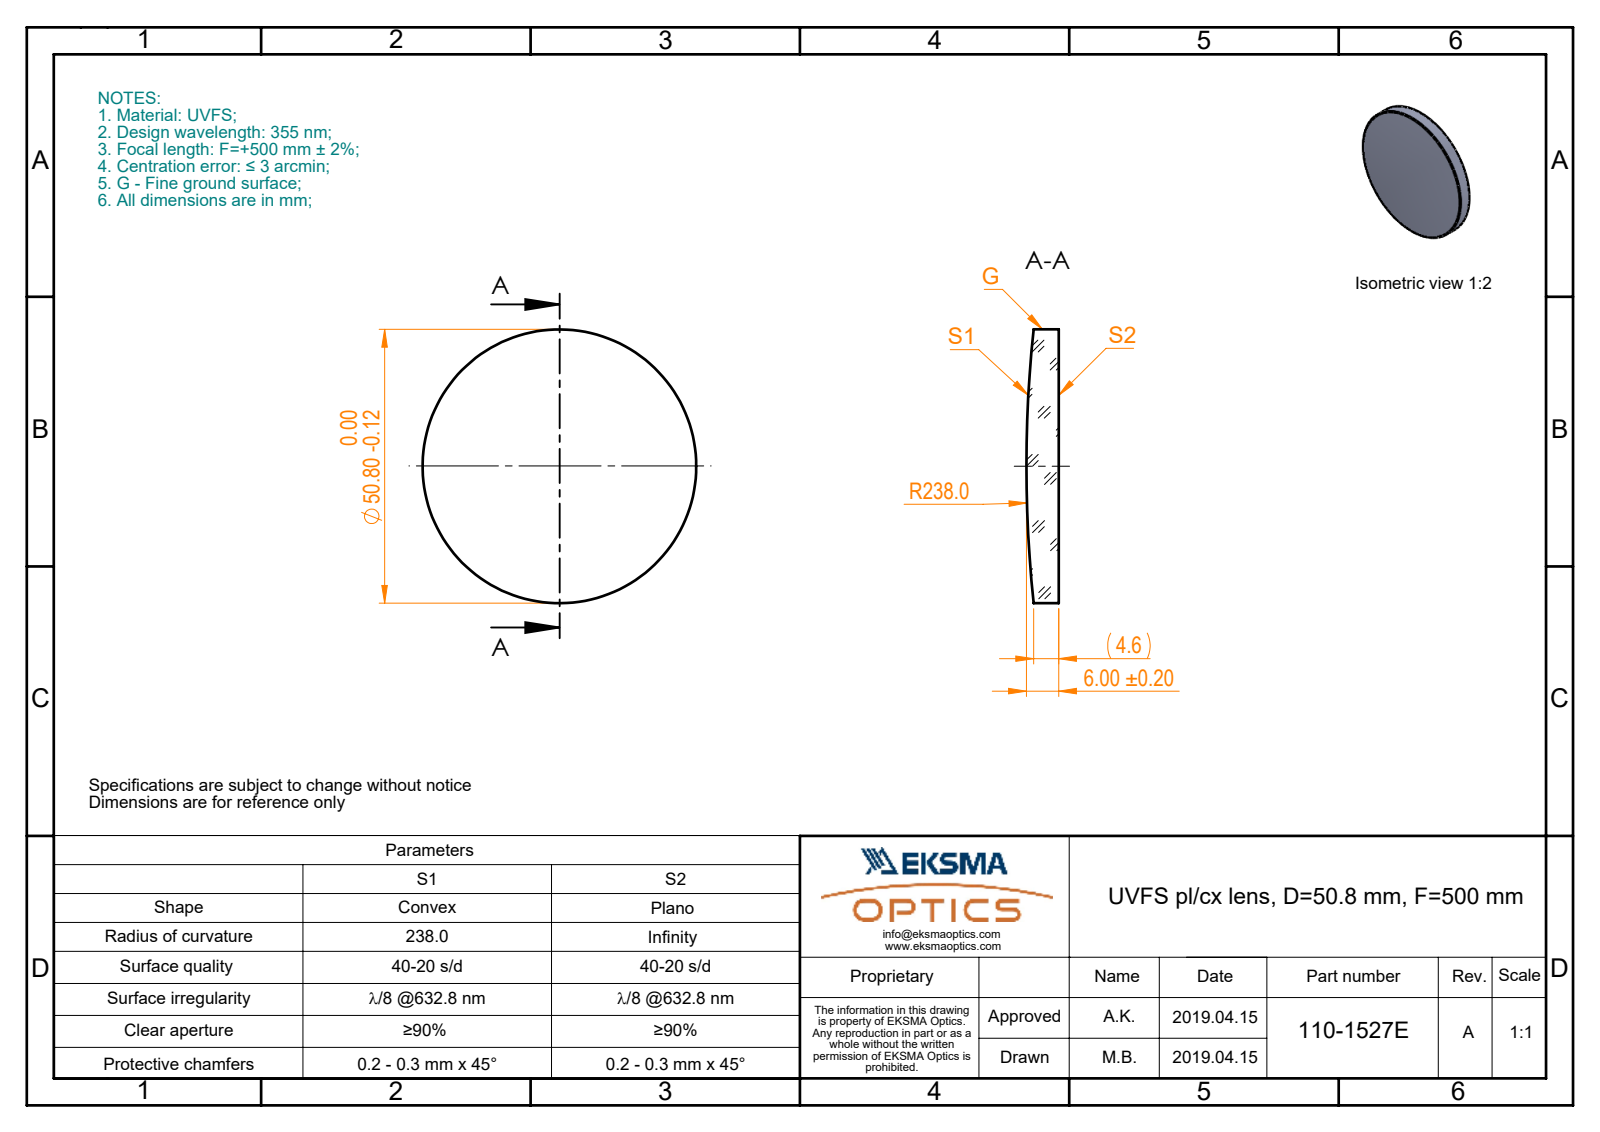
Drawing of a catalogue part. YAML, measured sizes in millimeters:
part_name: "110-1527E UVFS pl-cx 50.8 F500"
step_written_by: "SolidWorks 2017 (CONFIG_CONTROL_DESIGN)"
units: millimeters
bodies: {solids: 1, faces: 5, planar: 1, cylindrical: 2, other: 2}
overall_size: [50.8, 50.8, 6]
volume: 10785
surface_area: 4800
round_bosses_or_shafts:
  - {diameter: 50.8, count: 1}
